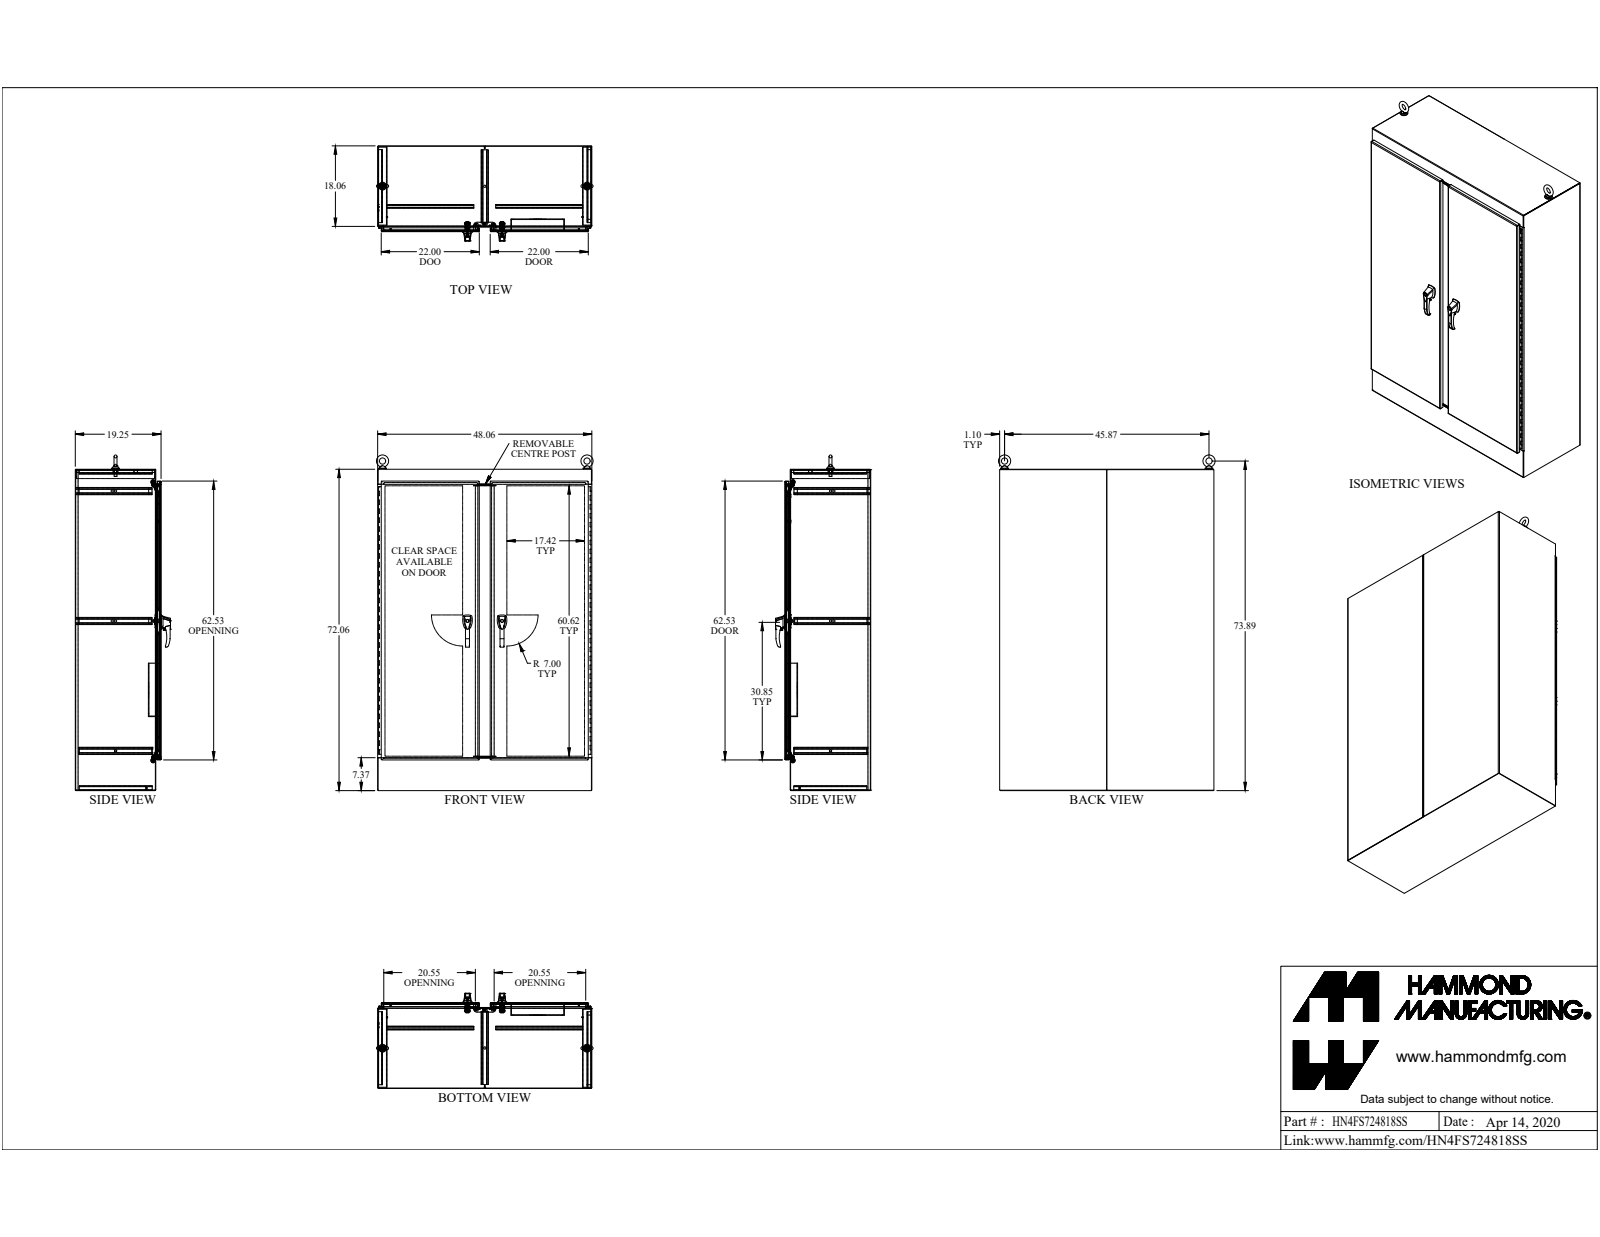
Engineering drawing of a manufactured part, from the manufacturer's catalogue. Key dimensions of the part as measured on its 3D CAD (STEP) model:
Part name (STEP PRODUCT): HN4FS724818SS
STEP written by: SolidWorks 2019 (CONFIG_CONTROL_DESIGN)
Units: inches
Bodies: 106 solids, 2965 faces (1563 planar, 1156 cylindrical, 246 other)
Overall size (bounding box): 75.256 × 48.604 × 21.362
Volume: 1 349 in³ · Surface area: 28 444 in²
Round holes (diameter × count): ⌀0.304 ×20, ⌀0.35 ×8, ⌀0.25 ×7, ⌀0.5 ×7, ⌀0.257 ×4, ⌀0.28 ×4, ⌀0.281 ×4, ⌀0.313 ×4, ⌀0.39 ×4, ⌀0.413 ×4, ⌀0.201 ×3, ⌀0.313 ×3
Round bosses / shafts (diameter × count): ⌀1 ×4, ⌀0.75 ×4, ⌀0.63 ×4, ⌀0.625 ×4, ⌀0.44 ×4, ⌀0.37 ×4, ⌀0.313 ×4, ⌀0.281 ×4
Partial cylindrical surfaces — rounded edges, fillets, slot ends (radius × count): R0.043 ×54, R0.138 ×48, R0.5 ×33, R0.1 ×28, R0.125 ×27, R0.06 ×24, R0.318 ×19, R0.017 ×16
Main face-to-face distances: 0.095, 19.152, 19.057, 19.247, 47.965, 71.965, 1.187, 17.965, 47.87, 48.06
Hole centre spacings: 6, 46.715, 12, 47.857, 18, 49.702, 24, 52.176
